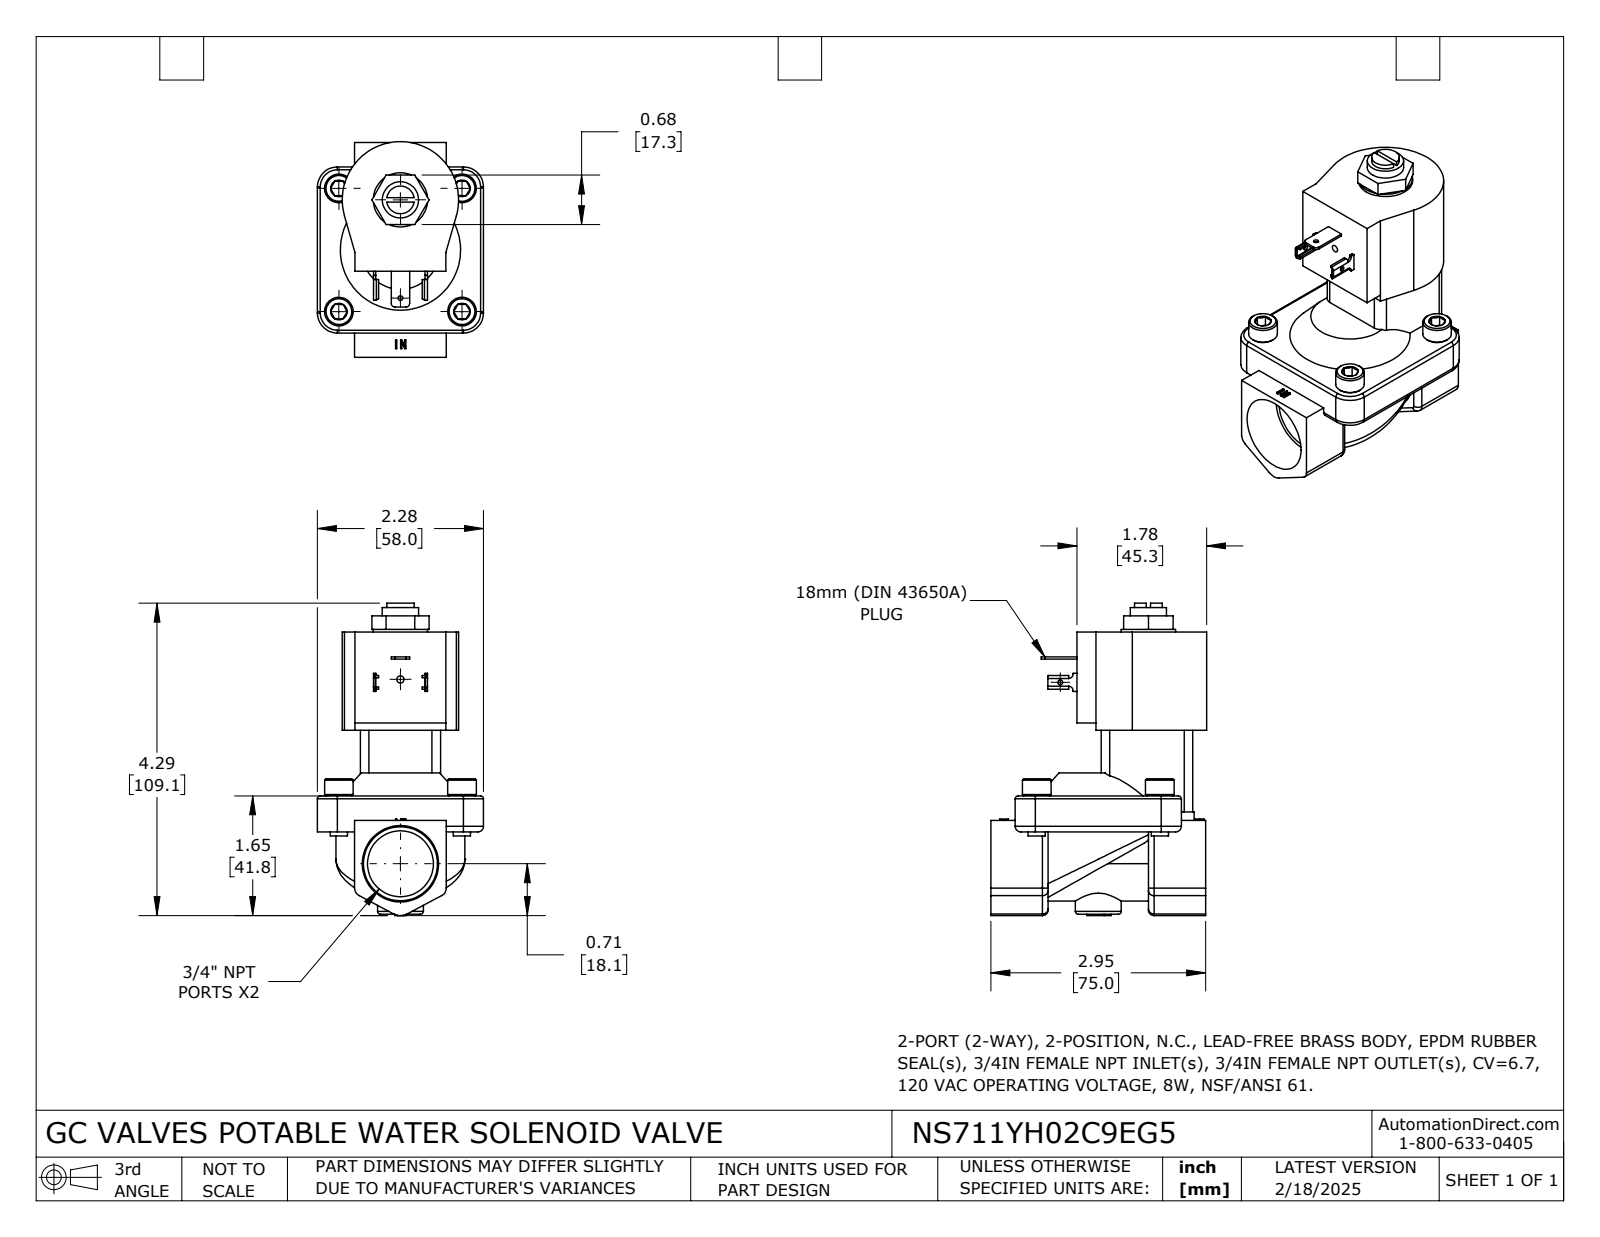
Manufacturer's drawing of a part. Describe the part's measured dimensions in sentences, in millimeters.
The part is named "NS711YH02C9EG5". Its 3-D file was written by "SolidWorks 2024 (CONFIG_CONTROL_DESIGN)". It is 1 solid with 366 faces: 189 planar, 92 cylindrical and 85 other. Overall it measures 109.07 by 75.32 by 58 millimeters. Its volume is 158 585 cubic millimeters and its surface area 32 388 square millimeters. Round holes: 1 of diameter 1.68, 1 of diameter 1.7, 1 of diameter 2.53, 1 of diameter 23.01, 1 of diameter 30.48. Round bosses or shafts: 4 of diameter 10, 4 of diameter 6, 1 of diameter 18.95, 1 of diameter 16, 1 of diameter 12.67, 1 of diameter 9.65. Partial cylindrical surfaces (rounded edges, fillets, slot ends): 11 of radius 2, 6 of radius 3, 4 of radius 0.15, 4 of radius 1, 4 of radius 1.04, 4 of radius 7, 2 of radius 1.27, 2 of radius 1.52. The main face-to-face distances are 30, 2, 57.19, 32, 22.9, 34.29, 43, 15, 13, 45. The hole center spacings are 34.29, 64.36.
